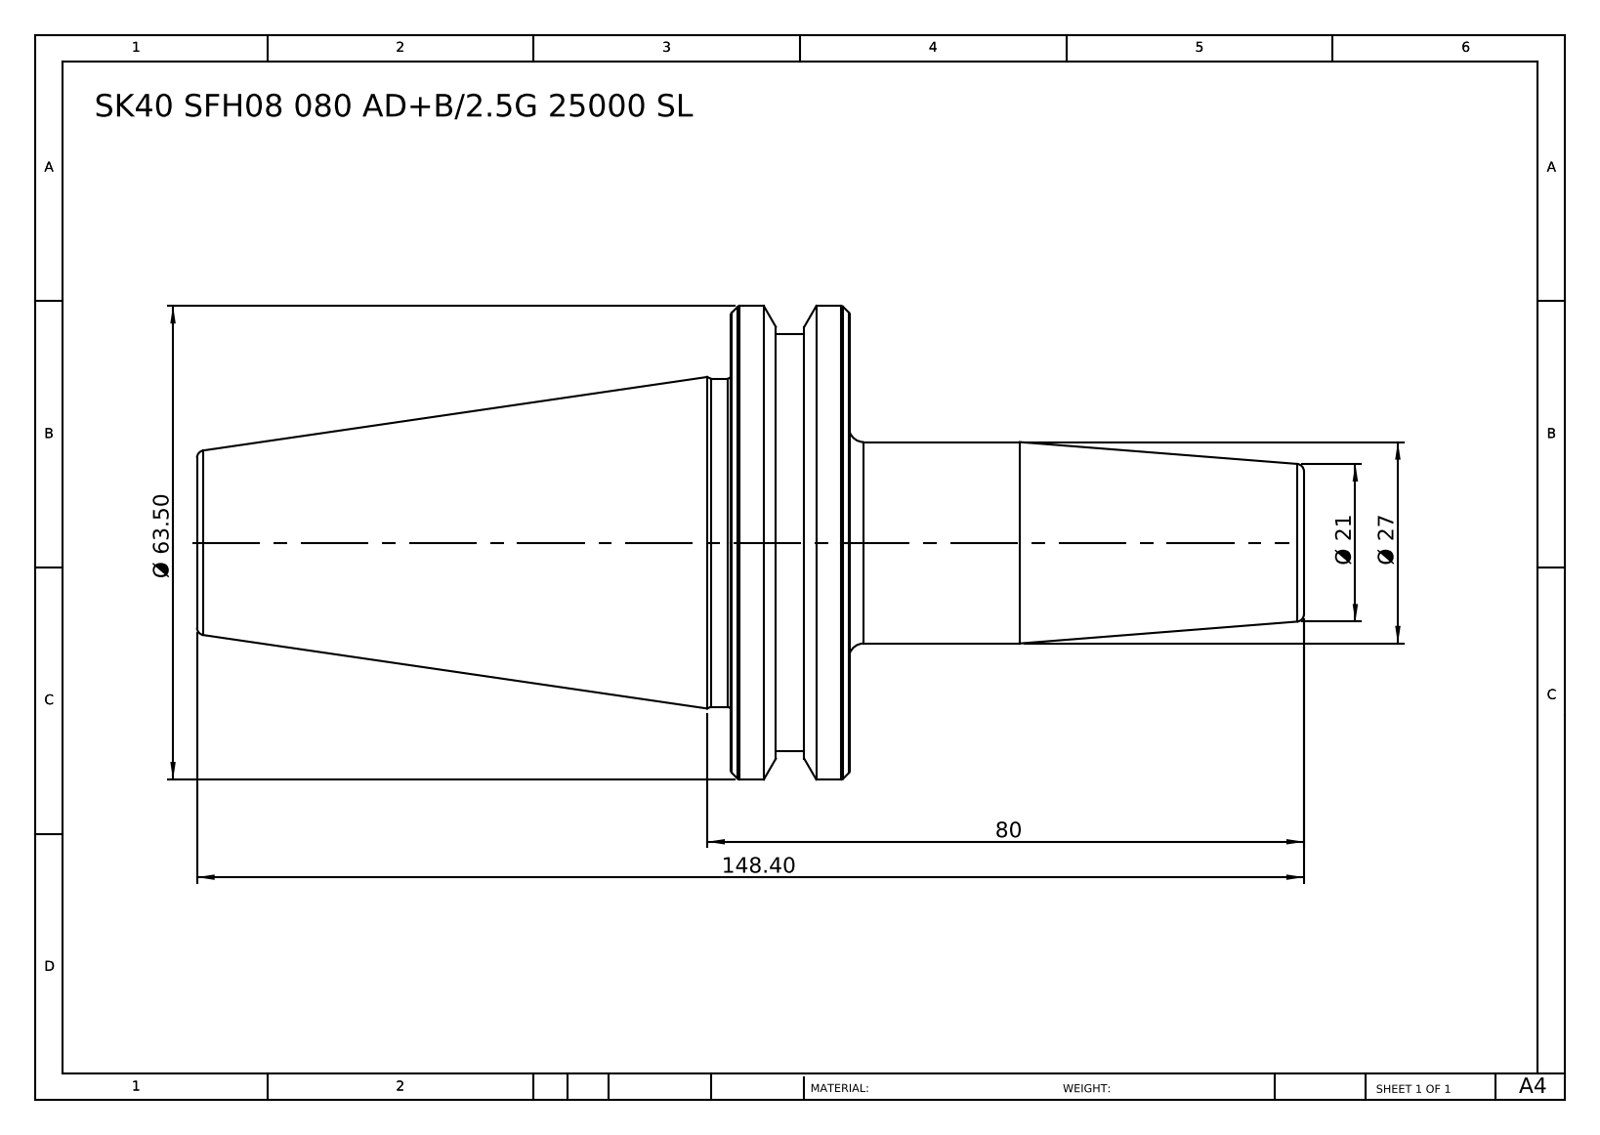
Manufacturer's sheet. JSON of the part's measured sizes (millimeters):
{"part_name": "SK40 SFH08 80 AD+B-2.5G 25000 SL", "step_written_by": "SolidWorks 2014 (CONFIG_CONTROL_DESIGN)", "units": "millimeters", "bodies": {"solids": 1, "faces": 46, "planar": 6, "cylindrical": 10, "other": 30}, "overall_size": [148.4, 63.5, 63.5], "volume_mm3": 147522, "surface_area_mm2": 21429, "round_bosses_or_shafts": [[63.5, 1], [56, 1], [44, 1], [27, 1]], "face_to_face_distances": [15.9, 87.5, 71.6, 60.9, 76.8, 148.4, 67, 6.1, 9.8, 81.4]}
